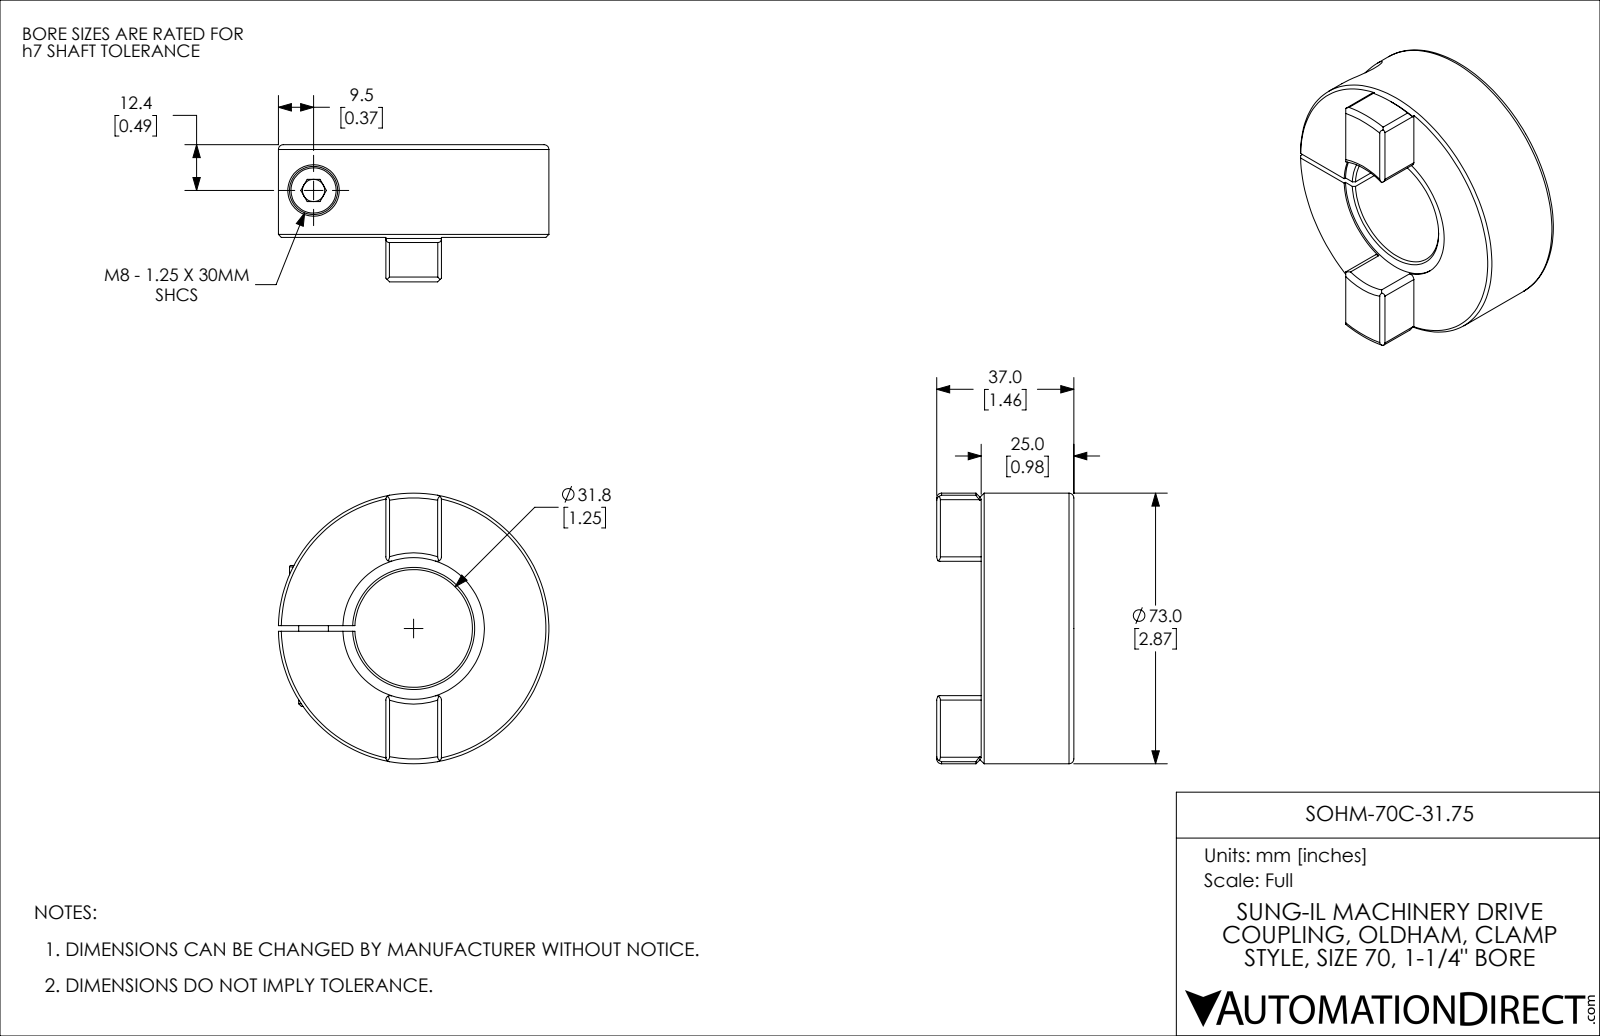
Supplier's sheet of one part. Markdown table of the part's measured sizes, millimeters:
| quantity | value |
| --- | --- |
| part name | SOHM-70C-31.75 |
| STEP written by | SolidWorks 2021 (CONFIG_CONTROL_DESIGN) |
| units | millimeters |
| bodies | 2 solids, 95 faces (35 planar, 30 cylindrical, 30 other) |
| overall size | 73 × 73 × 37 |
| volume | 88 690 mm³ |
| surface area | 19 630 mm² |
| round holes (diameter × count) | 6 × 1, 6.8 × 1, 8.5 × 1, 13.9 × 1, 31.8 × 1, 38.2 × 1 |
| round bosses / shafts (diameter × count) | 73 × 1, 13 × 1, 8 × 1 |
| partial cylindrical surfaces (radius × count) | 1.2 × 8, 50 × 1 |
| main face-to-face distances | 25, 1.5, 37, 12, 15, 24.5, 0.5, 12.5, 9.8, 8.3 |
